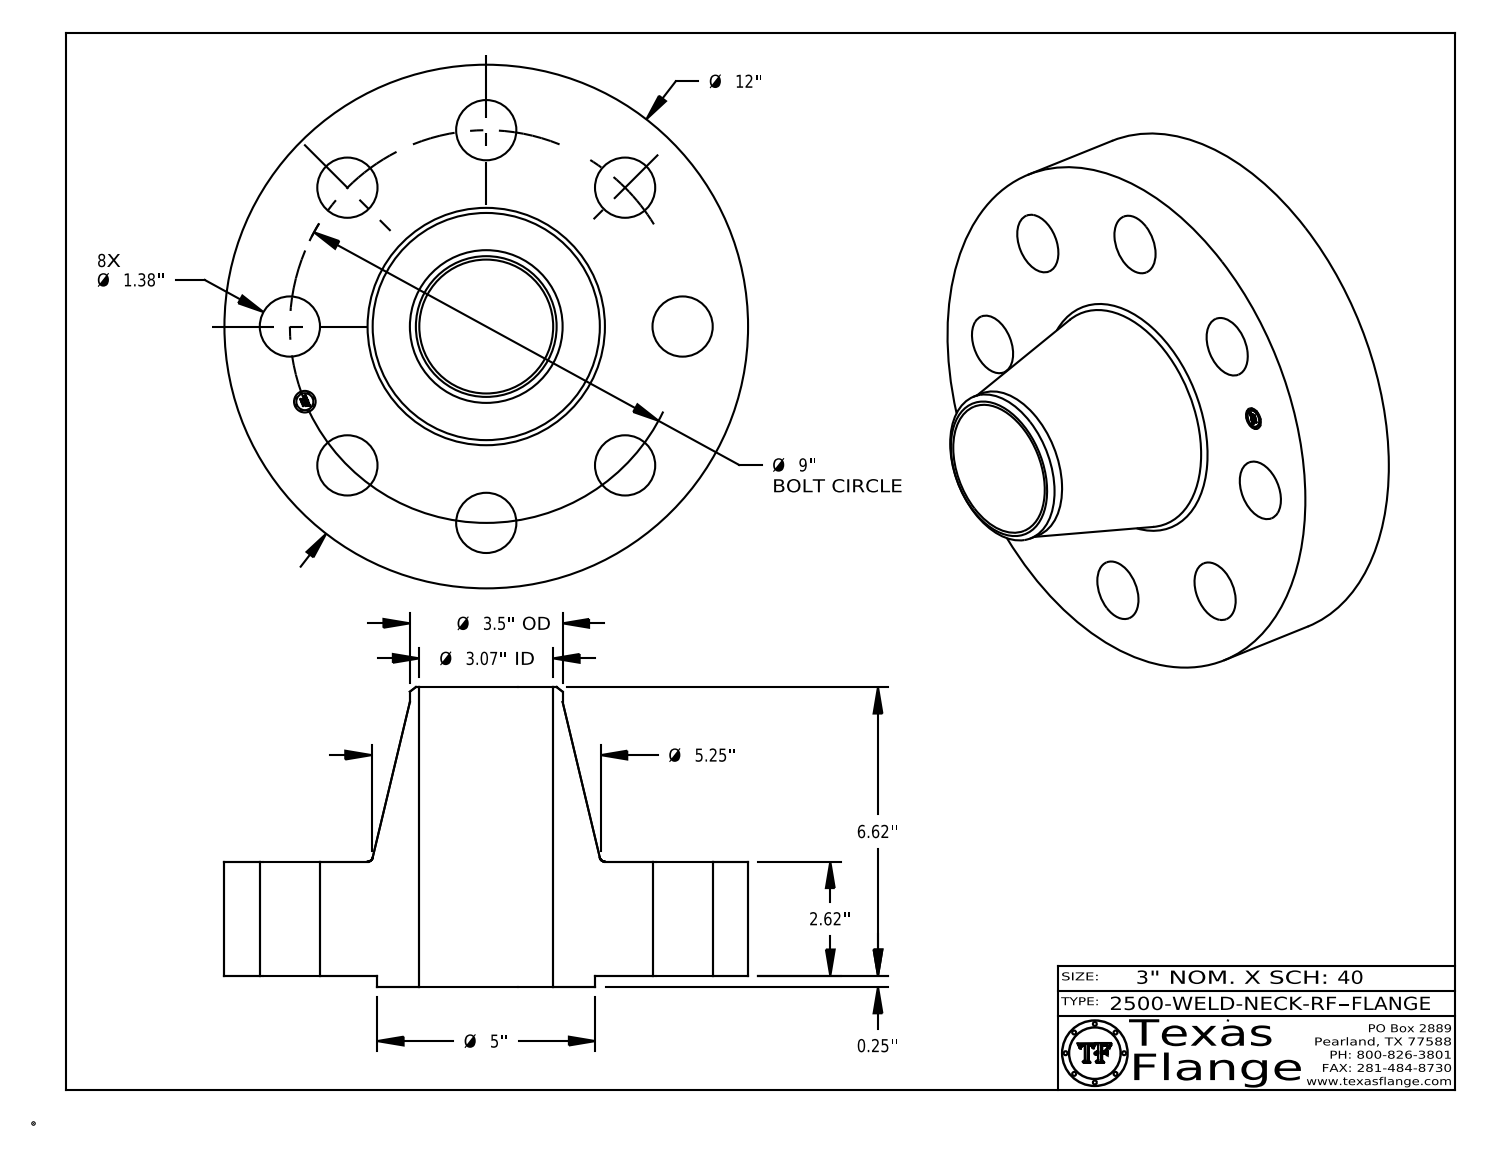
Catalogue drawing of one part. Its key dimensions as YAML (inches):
part_name: "2500-WELD-NECK-RF"
step_written_by: "CATIA V5 STEP AP214 (AUTOMOTIVE_DESIGN)"
units: inches
bodies: {solids: 1, faces: 419, planar: 369, cylindrical: 44, other: 6}
overall_size: [12, 12, 6.87]
volume: 278.1
surface_area: 489.5
round_holes:
  - {diameter: 1.38, count: 8}
  - {diameter: 0.495, count: 1}
  - {diameter: 3.068, count: 1}
round_bosses_or_shafts:
  - {diameter: 0.03, count: 8}
  - {diameter: 12, count: 1}
  - {diameter: 5, count: 1}
  - {diameter: 3.5, count: 1}
  - {diameter: 0.39, count: 1}
face_to_face_distances: [2.62, 0.25, 2.87, 6.87, 6.62, 4, 2.855, 2.605, 0.015, 4.015]
hole_center_spacings: [4.5, 3.444, 6.364, 8.315, 1.756, 5, 7.483, 9]
